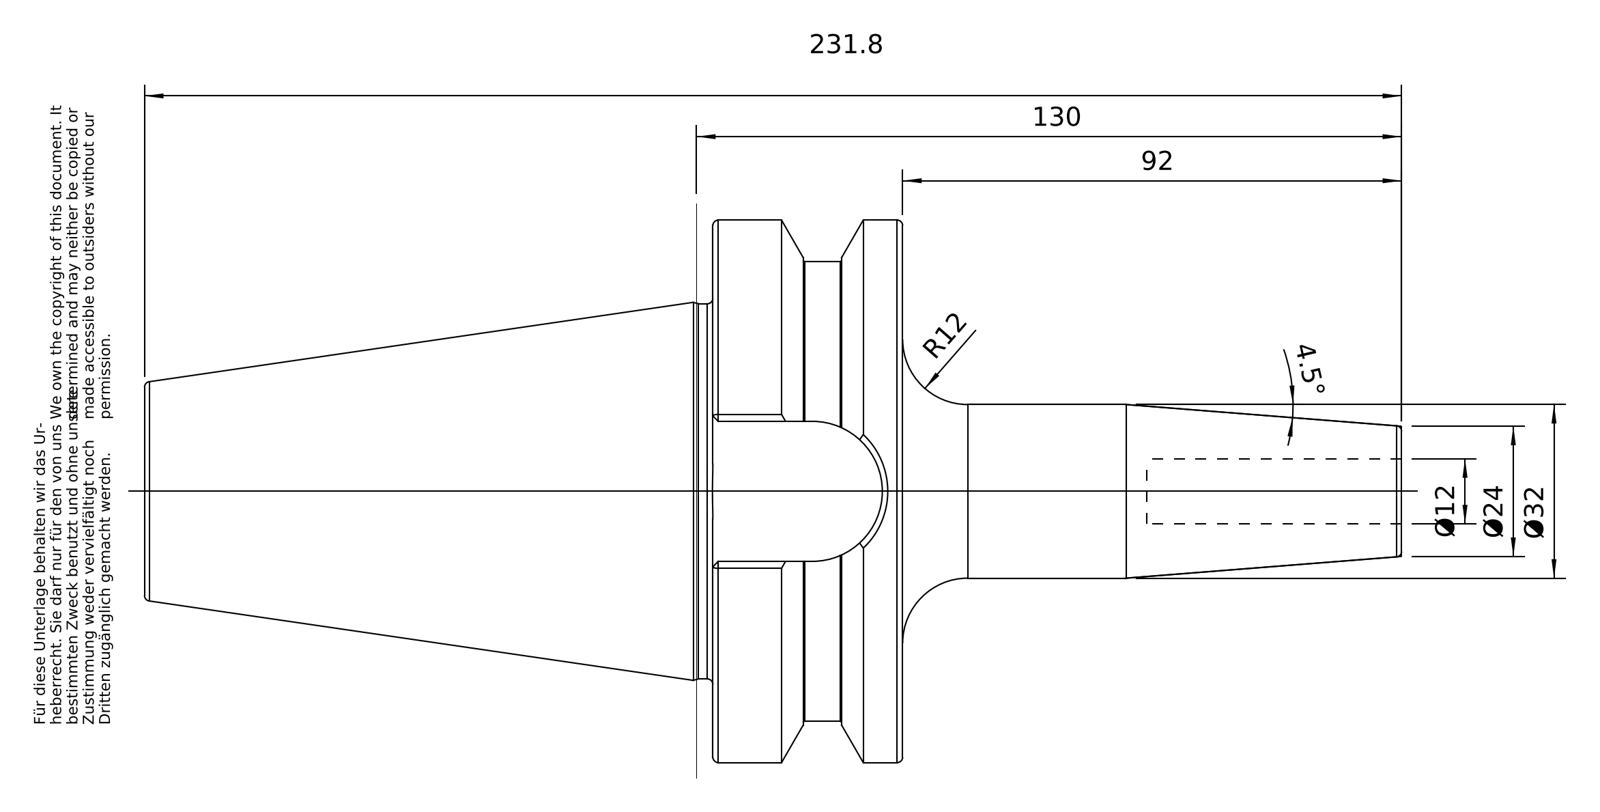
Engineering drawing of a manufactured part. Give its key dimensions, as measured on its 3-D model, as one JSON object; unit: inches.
{"part_name": "50-644-12", "step_written_by": "PRO/ENGINEER BY PARAMETRIC TECHNOLOGY CORPORATION, 2010430 (CONFIG_CONTROL_DESIGN)", "units": "inches", "bodies": {"solids": 1, "faces": 96, "planar": 26, "cylindrical": 22, "other": 48}, "overall_size": [9.126, 3.936, 3.936], "volume_in3": 32.4, "surface_area_in2": 95.19, "round_holes": [[0.472, 1], [0.817, 1], [0.985, 1], [1.012, 1]], "round_bosses_or_shafts": [[3.936, 1], [3.337, 1], [2.722, 1], [1.26, 1], [0.945, 1]], "partial_cylinders_radius": [[0.508, 1]], "face_to_face_distances": [1.378, 2.772, 4.126, 5.504, 1.016, 9.126, 5, 3.622, 1.89, 2.236]}
